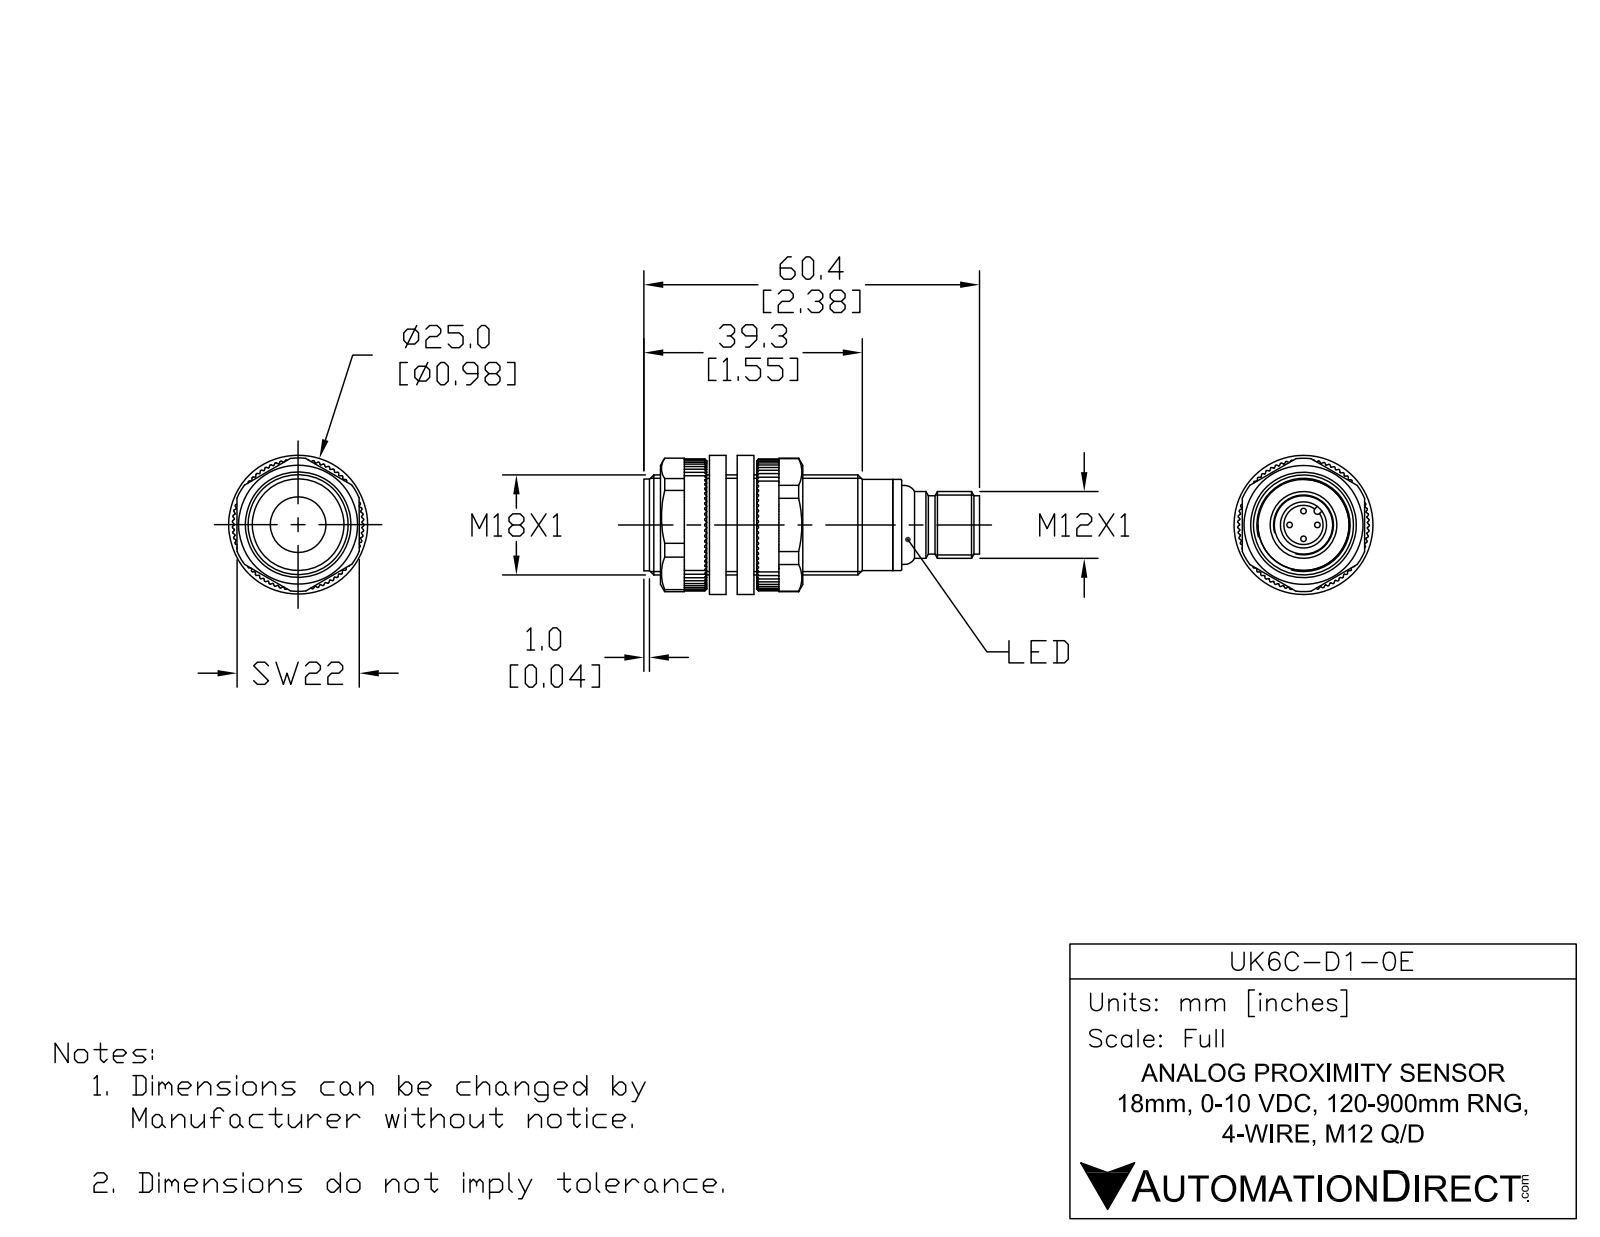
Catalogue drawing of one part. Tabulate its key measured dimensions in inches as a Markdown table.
| quantity | value |
| --- | --- |
| part name | UK6C-D1-0E |
| STEP written by | SolidWorks 2017 (AUTOMOTIVE_DESIGN) |
| units | inches |
| bodies | 4 solids, 86 faces (15 planar, 36 cylindrical, 35 other) |
| overall size | 2.374 × 0.709 × 0.709 |
| volume | 0.759 in³ |
| surface area | 7.648 in² |
| round holes (diameter × count) | 0.276 × 1, 0.327 × 1, 0.374 × 1 |
| round bosses / shafts (diameter × count) | 0.039 × 4, 0.709 × 1, 0.646 × 1, 0.622 × 1, 0.559 × 1, 0.472 × 1, 0.413 × 1 |
| partial cylindrical surfaces (radius × count) | 0.024 × 1 |
| main face-to-face distances | 1.724, 0.039, 1.764, 0.039, 1.763, 1.823, 1.822, 1.783, 0.059, 2.024 |
